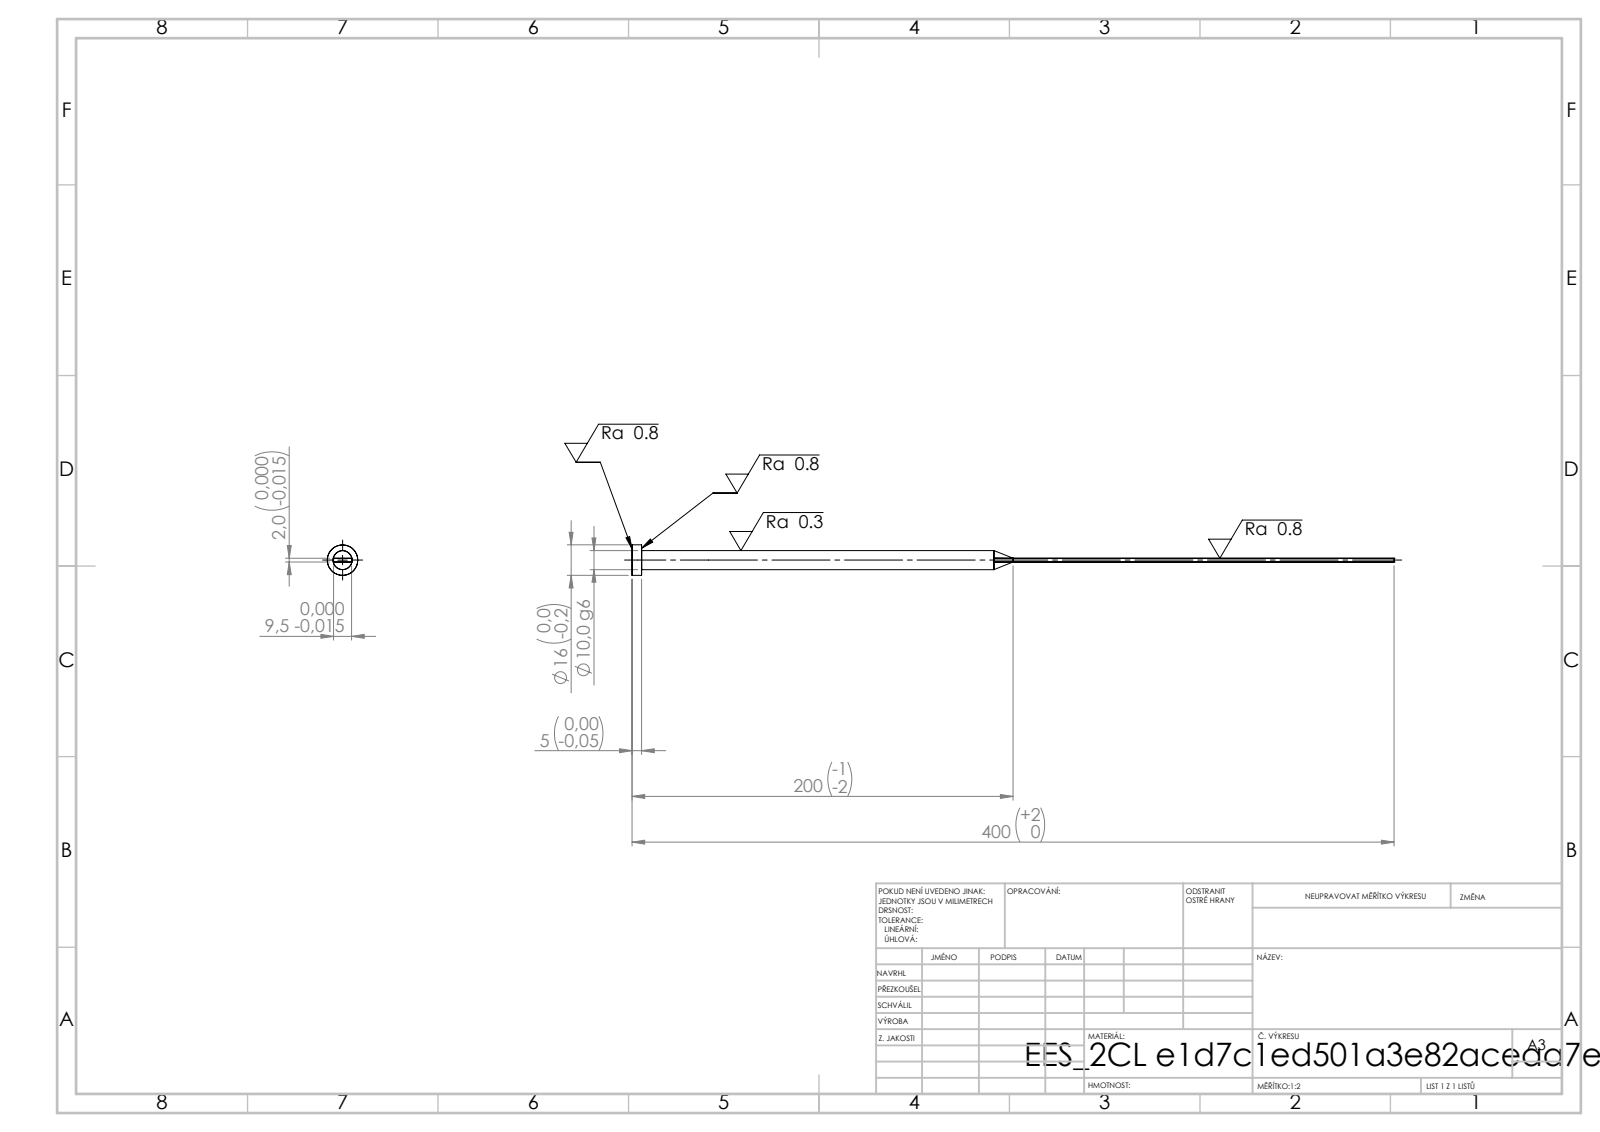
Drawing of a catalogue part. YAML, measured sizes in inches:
step_written_by: "SolidWorks 2019 (CONFIG_CONTROL_DESIGN)"
units: inches
bodies: {solids: 1, faces: 15, planar: 7, cylindrical: 4, other: 4}
overall_size: [15.748, 0.63, 0.63]
volume: 1.208
surface_area: 17.48
round_bosses_or_shafts:
  - {diameter: 0.63, count: 1}
  - {diameter: 0.394, count: 1}
face_to_face_distances: [0.079, 0.374, 0.197, 15.748, 15.551]
